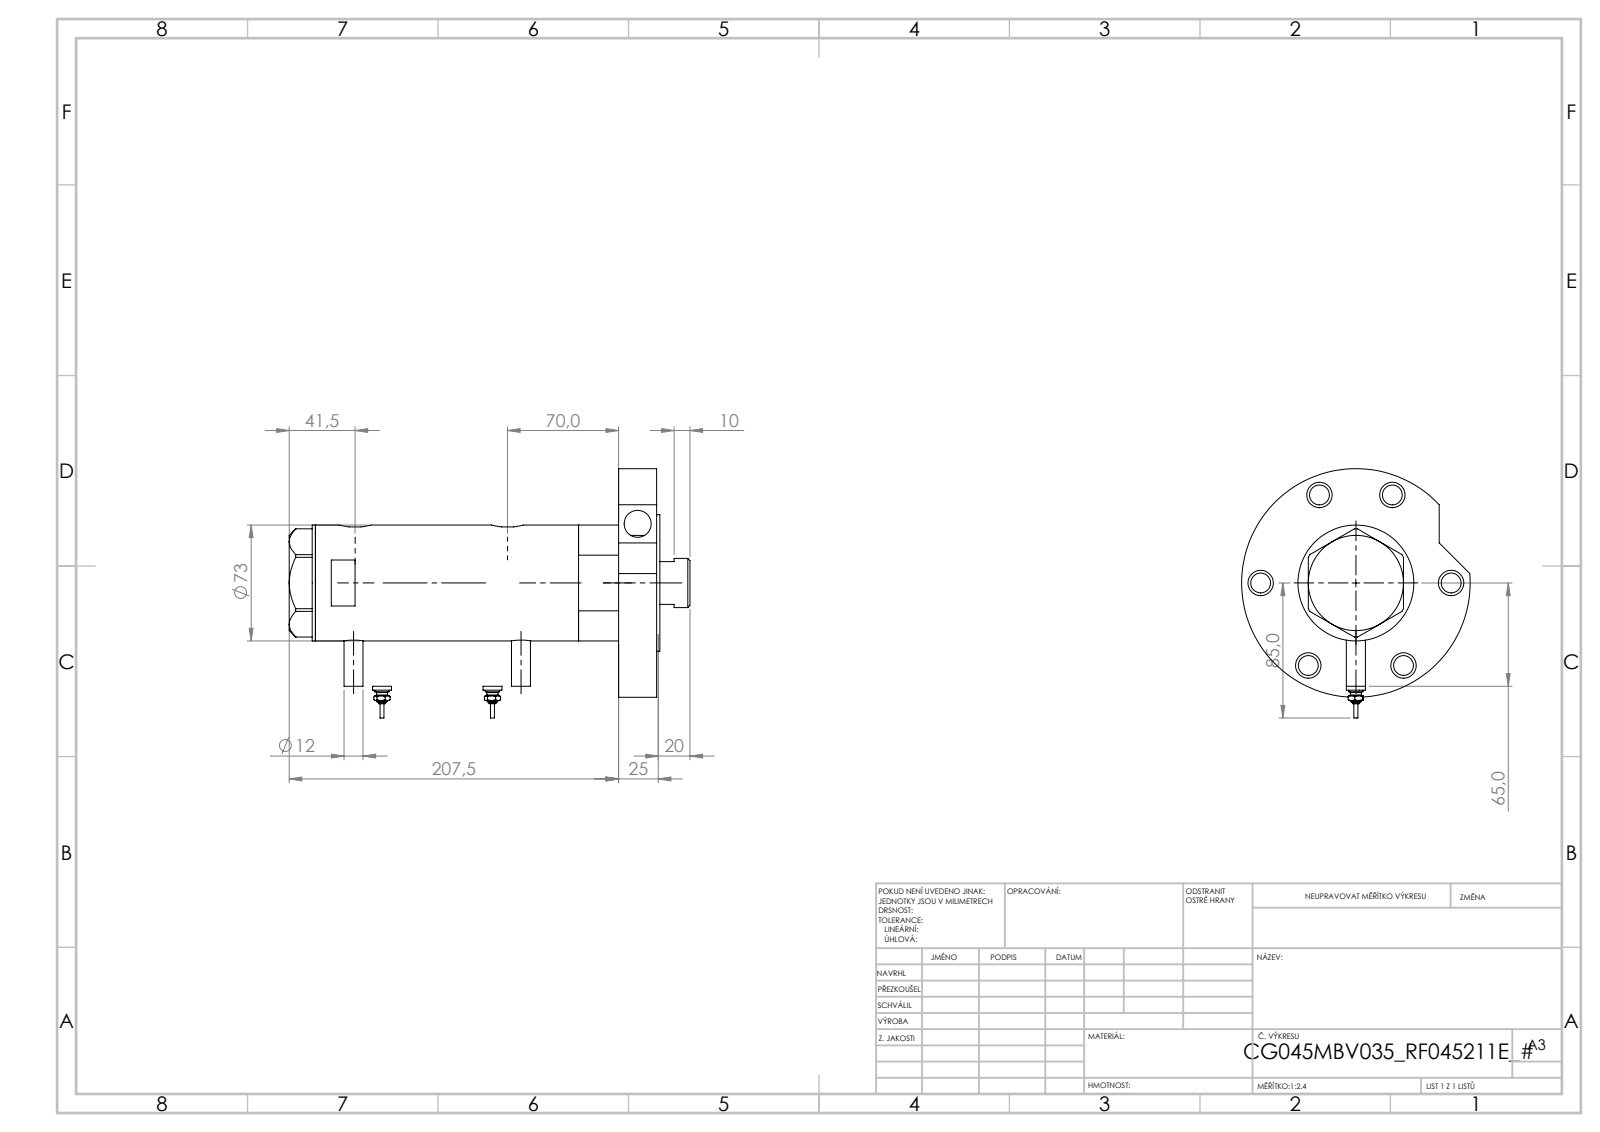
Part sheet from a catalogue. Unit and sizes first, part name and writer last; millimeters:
Units: millimetres
Overall size (bounding box): 226.52 × 144 × 144
Round holes (diameter × count): ⌀12.5 ×8, ⌀16 ×6, ⌀5 ×2, ⌀13.16 ×2, ⌀10.5 ×1, ⌀17 ×1, ⌀32 ×1, ⌀33.5 ×1, ⌀45 ×1, ⌀48 ×1, ⌀60 ×1, ⌀64 ×1
Round bosses / shafts (diameter × count): ⌀12 ×2, ⌀9 ×2, ⌀7 ×2, ⌀5 ×2, ⌀4.34 ×2, ⌀2.4 ×2, ⌀144 ×1, ⌀86 ×1
Partial cylindrical surfaces — rounded edges, fillets, slot ends (radius × count): R10 ×2
Main face-to-face distances: 24, 162.44, 26, 186.44, 2, 188.44, 76.15, 16.5, 178.94, 202.94
Hole centre spacings: 60, 66.67, 86.65, 99.77, 103.92, 107.62, 119.74, 0.99
Volume: 1 062 000 mm³ · Surface area: 190 891 mm²
Bodies: 7 solids, 275 faces (89 planar, 112 cylindrical, 74 other)
Part name (STEP PRODUCT): V270CG_VC; V270CG_BACK; V270CG_MIDDLE; V270CG_SWITCH (+2 more)
STEP written by: SolidWorks 2019 (CONFIG_CONTROL_DESIGN)
